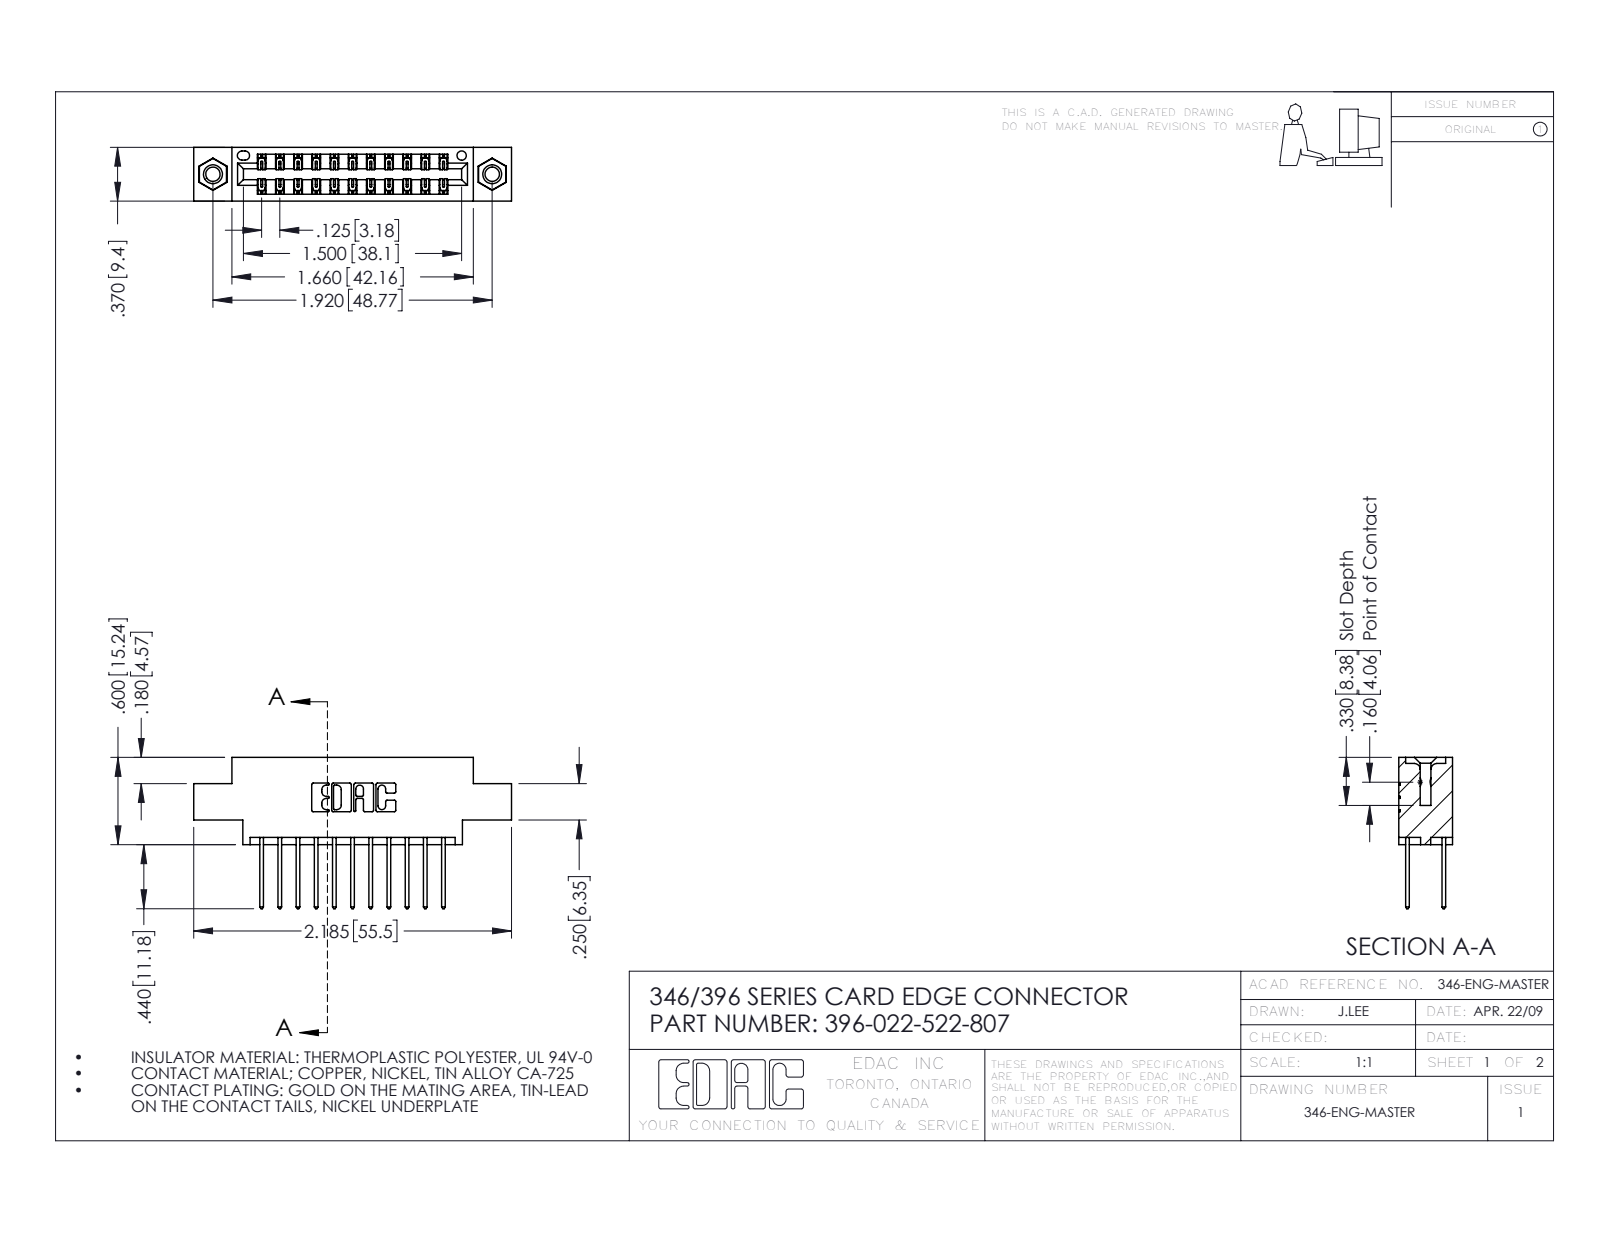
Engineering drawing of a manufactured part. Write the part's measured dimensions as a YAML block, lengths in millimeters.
part_name: "345-292-001_345-293-122; 346 Part_0.170 Offset - 0.156 Dia-TI; 345-250-001_345-250-005-103; 396-022-522-807"
step_written_by: "SolidWorks 2016 (CONFIG_CONTROL_DESIGN)"
units: millimeters
bodies: {solids: 25, faces: 1330, planar: 882, cylindrical: 432, other: 16}
overall_size: [55.5, 26.4, 9.4]
volume: 5060
surface_area: 6942
round_holes:
  - {diameter: 2.5, count: 2}
  - {diameter: 3.2, count: 2}
  - {diameter: 4, count: 2}
  - {diameter: 1.6, count: 1}
round_bosses_or_shafts:
  - {diameter: 3.9, count: 2}
partial_cylinders:
  - {radius: 0.2, count: 33}
  - {radius: 0.3, count: 22}
  - {radius: 0.3, count: 22}
  - {radius: 0.2, count: 6}
  - {radius: 0.8, count: 6}
  - {radius: 0.7, count: 3}
  - {radius: 0.4, count: 2}
  - {radius: 0.6, count: 2}
face_to_face_distances: [6.4, 1.2, 8.2, 9.4, 1.8, 7.6, 0.6, 7, 5.6, 3.8]
hole_center_spacings: [6.2, 43.6, 48.8]
